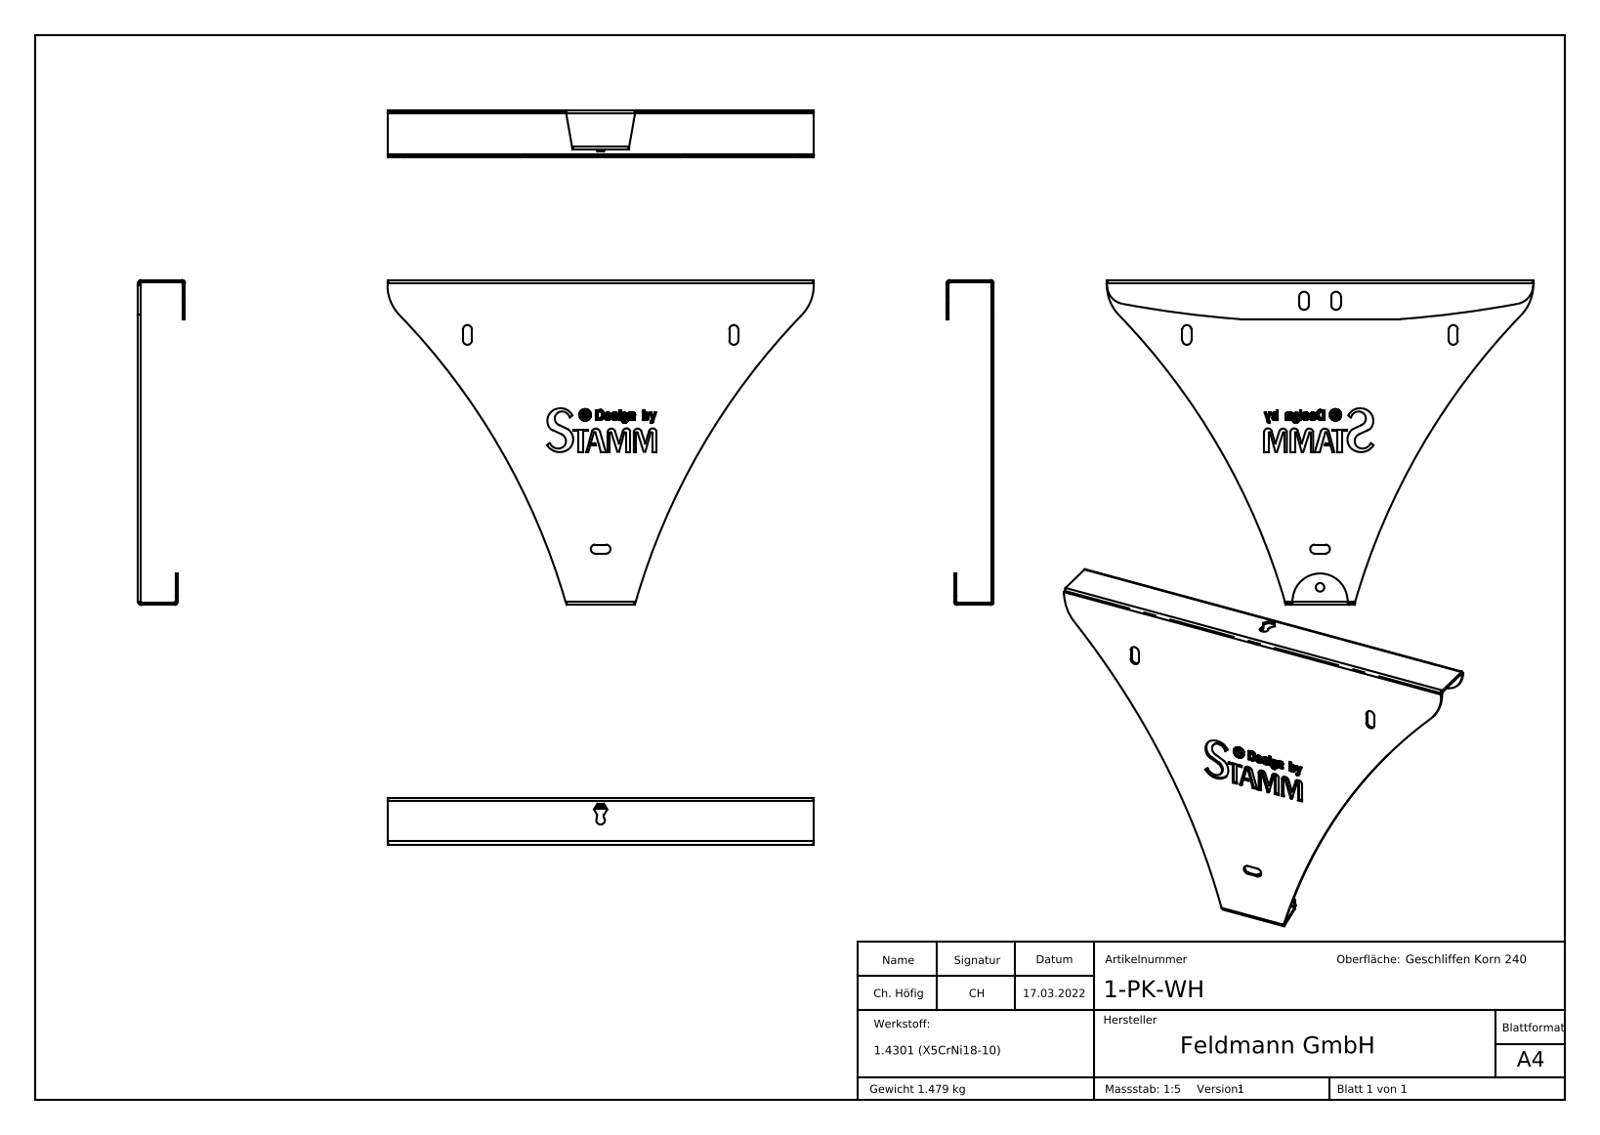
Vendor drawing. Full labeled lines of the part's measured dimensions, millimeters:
Part name (STEP PRODUCT): 1-PK-WH
STEP written by: SolidWorks 2018 (CONFIG_CONTROL_DESIGN)
Units: millimetres
Bodies: 1 solid, 1529 faces (1368 planar, 55 cylindrical, 106 other)
Overall size (bounding box): 400 × 304.8 × 43.86
Volume: 187 260 mm³ · Surface area: 192 740 mm²
Round holes (diameter × count): ⌀8 ×1
Partial cylindrical surfaces — rounded edges, fillets, slot ends (radius × count): R4.25 ×6, R0.71 ×4, R0.71 ×4, R1 ×4, R3 ×4, R3.6 ×4, R4.5 ×4, R0.14 ×2
Main face-to-face distances: 2, 41.86, 39.86, 43.86, 302.79, 34.87, 6.99, 304.79, 300.79, 36.87
